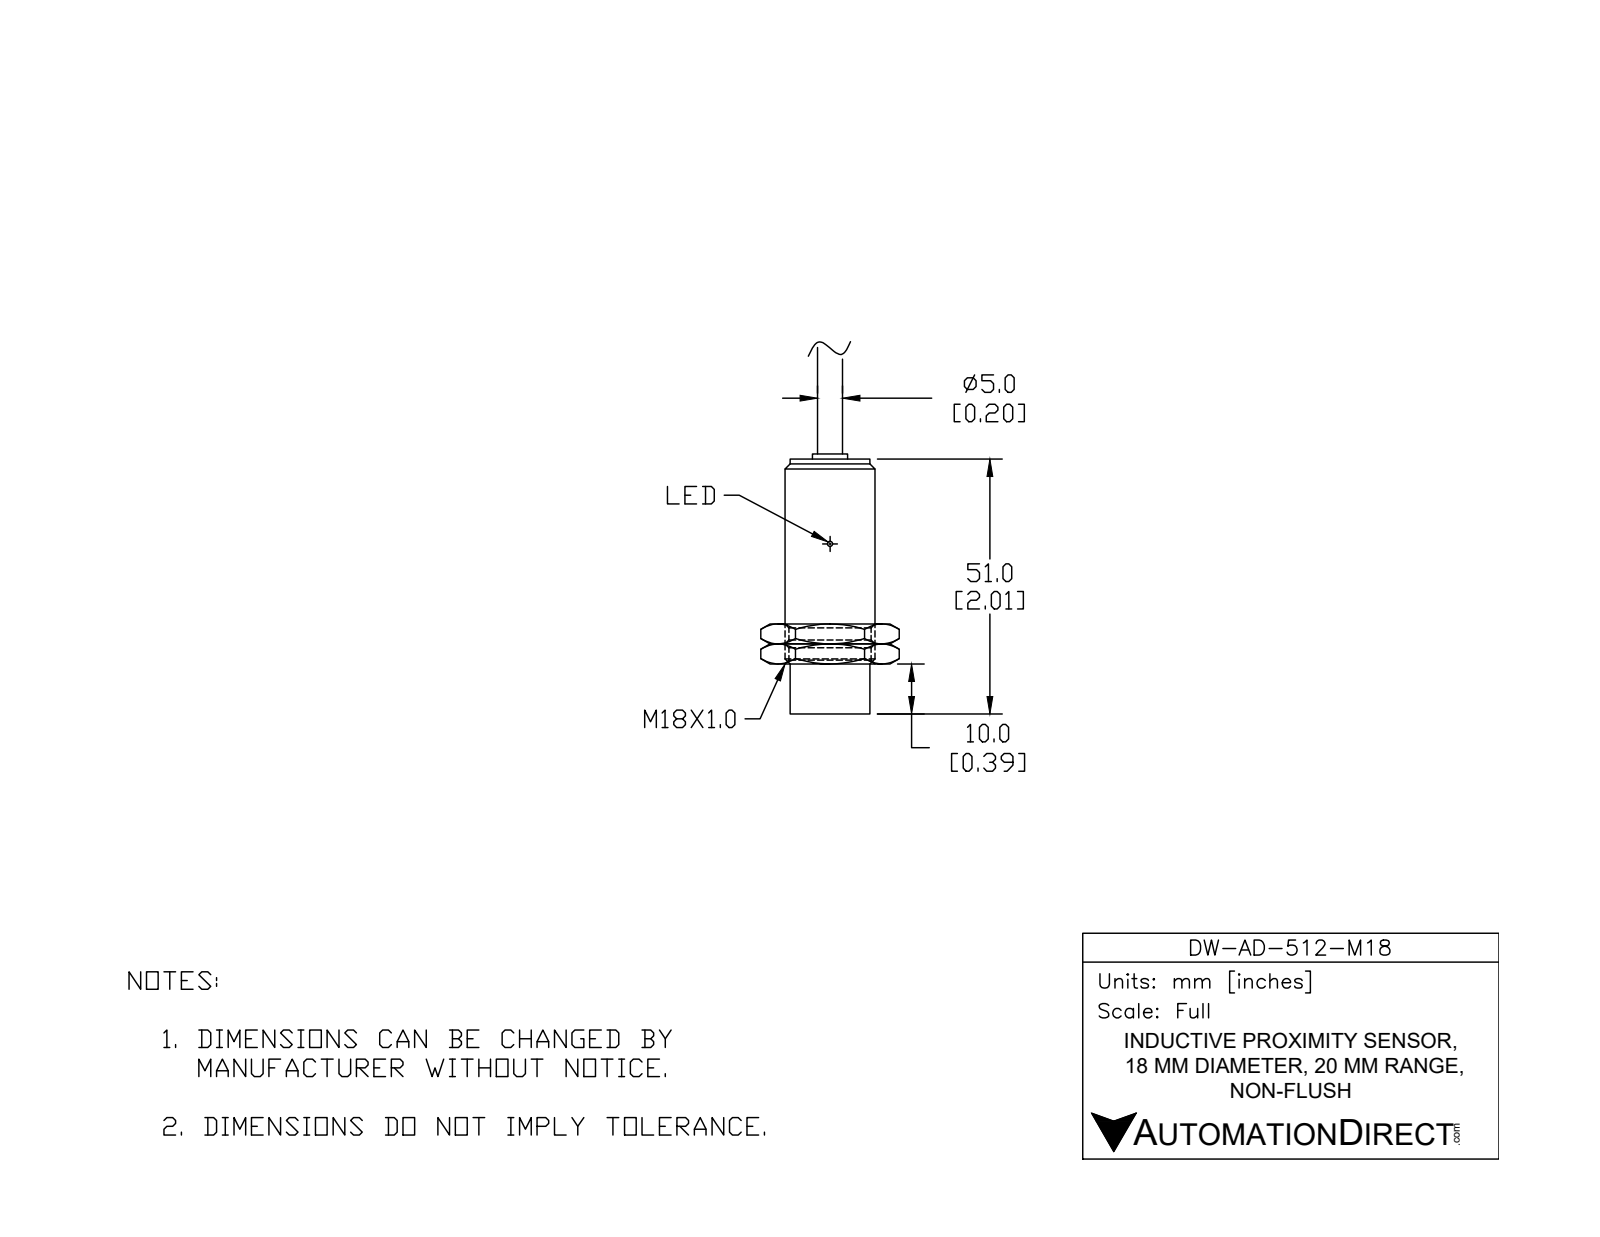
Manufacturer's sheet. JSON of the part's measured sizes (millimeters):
{"part_name": "DW-AD-512-M18", "step_written_by": "SolidWorks 2017 (AUTOMOTIVE_DESIGN)", "units": "millimeters", "bodies": {"solids": 2, "faces": 37, "planar": 18, "cylindrical": 7, "other": 12}, "overall_size": [76.6, 18, 18], "volume_mm3": 13200, "surface_area_mm2": 3815, "round_bosses_or_shafts": [[18, 1], [16.5, 1], [16.4, 1], [10.5, 1], [6.8, 1], [5, 1], [3, 1]], "face_to_face_distances": [51, 0.8, 53, 2, 51.8, 1.2, 48, 3, 3.8, 5]}
